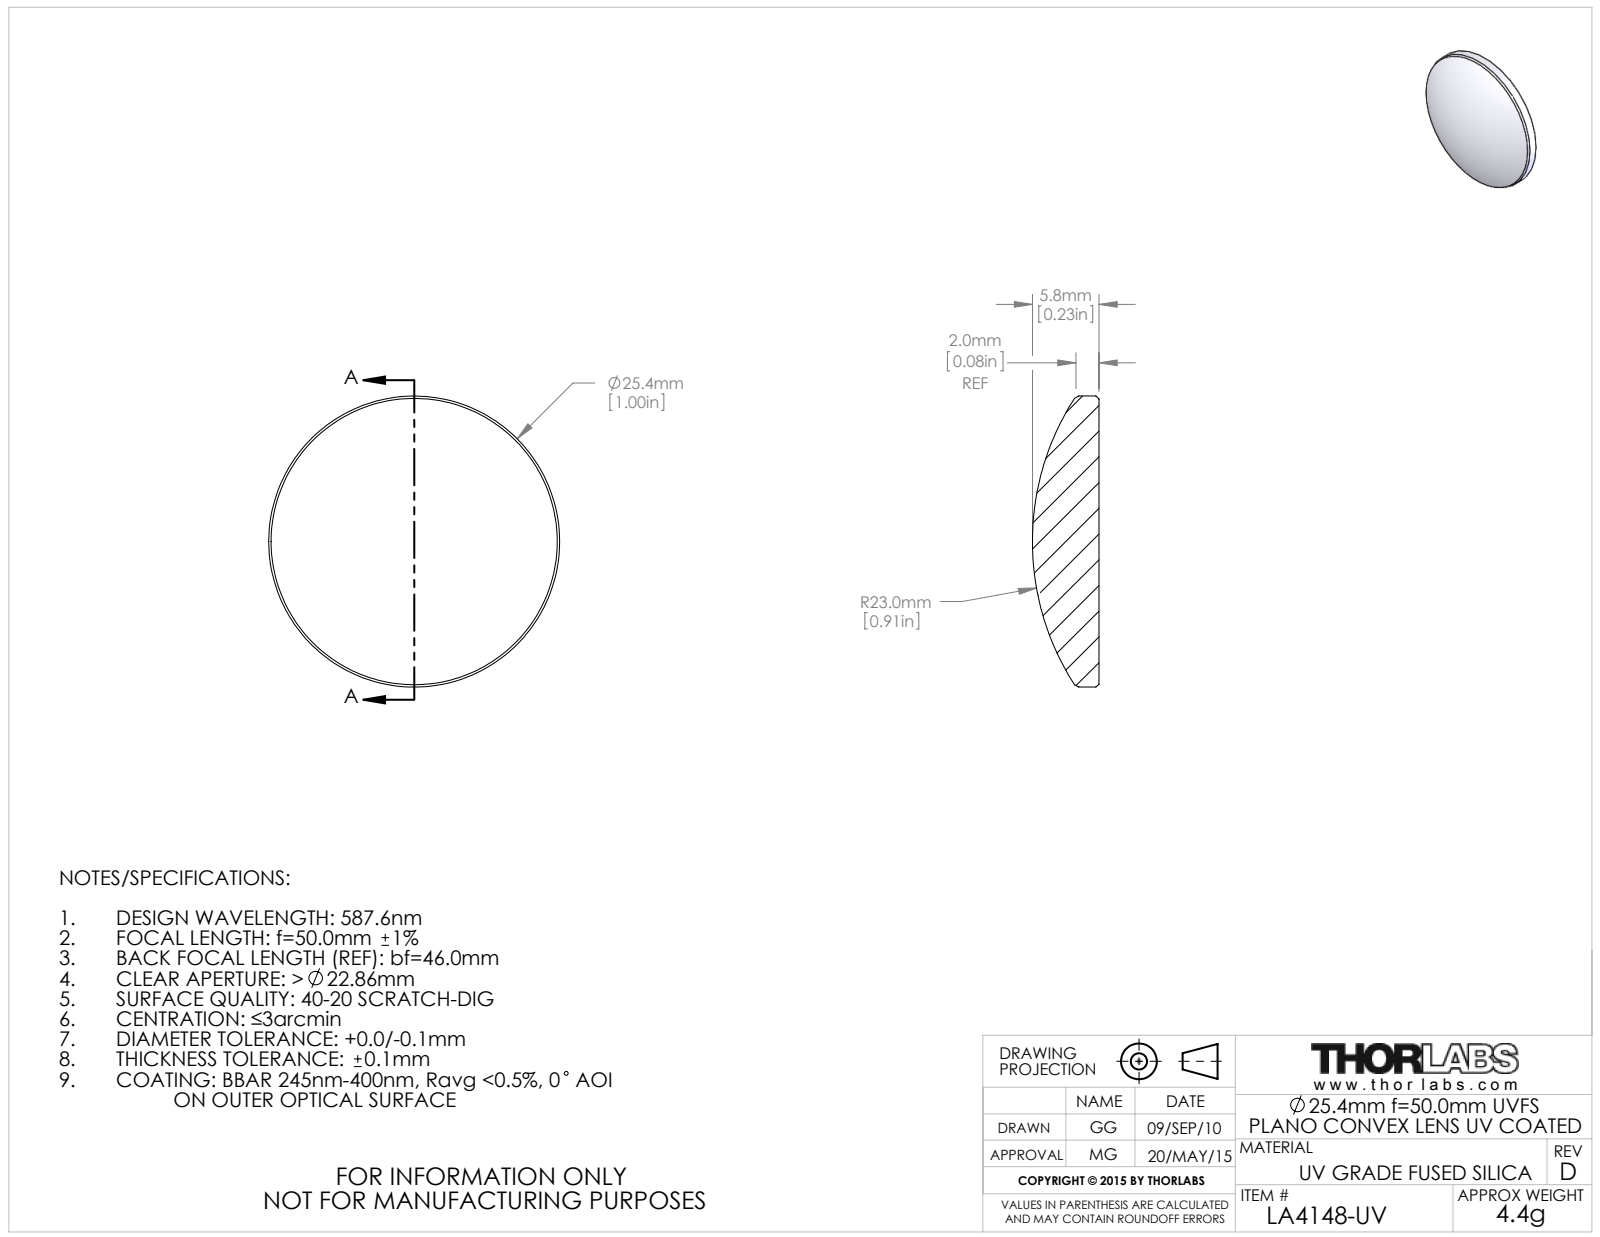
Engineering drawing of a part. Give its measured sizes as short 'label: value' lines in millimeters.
name: 4280-E0W
written by: SolidWorks 2014 (CONFIG_CONTROL_DESIGN)
unit: mm
bodies: 1 solid, 9 faces (1 planar, 2 cylindrical, 6 other)
size: 25.4 × 25.4 × 5.8
volume: 2 002 mm³; area: 1 202 mm²
bosses: 1× ⌀25.4
